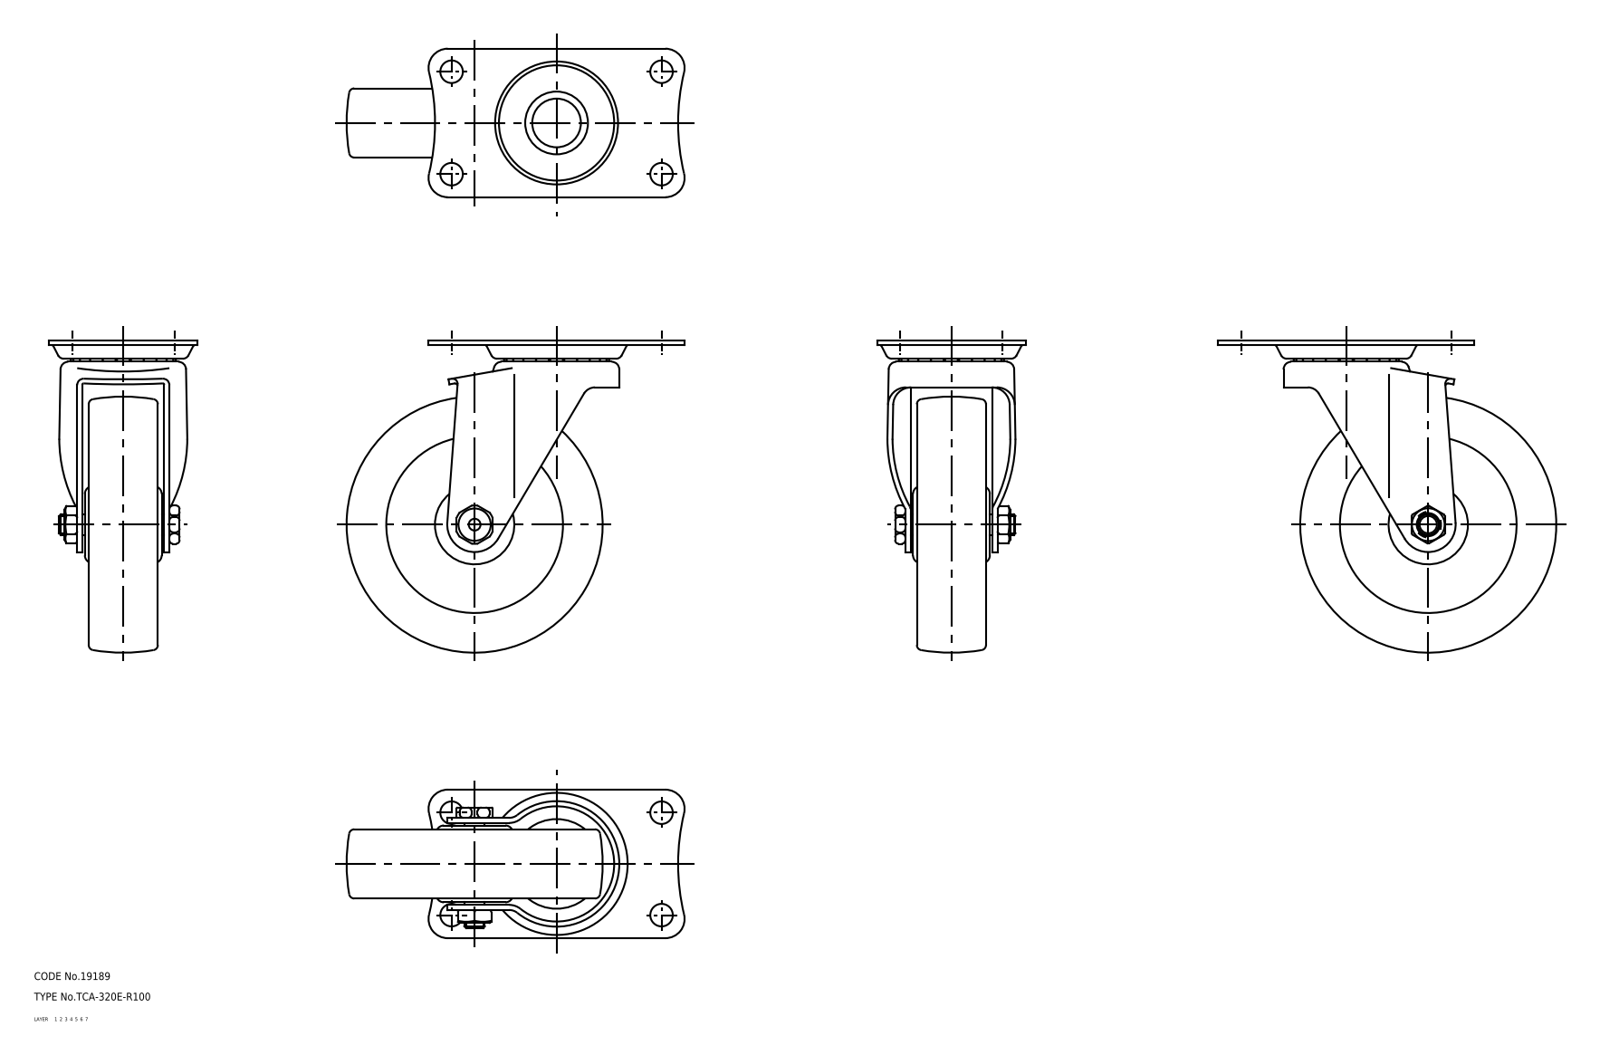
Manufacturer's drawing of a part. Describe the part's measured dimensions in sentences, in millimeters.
The part is named "wheel; mounting plate; main shaft; axle (+1 more)". Its 3-D file was written by "CADfix (AUTOMOTIVE_DESIGN)". It is 5 solids with 253 faces: 0 planar, 0 cylindrical and 253 other. Overall it measures 132 by 122 by 58 millimeters. Its volume is 242 802 cubic millimeters and its surface area 59 723 square millimeters.
